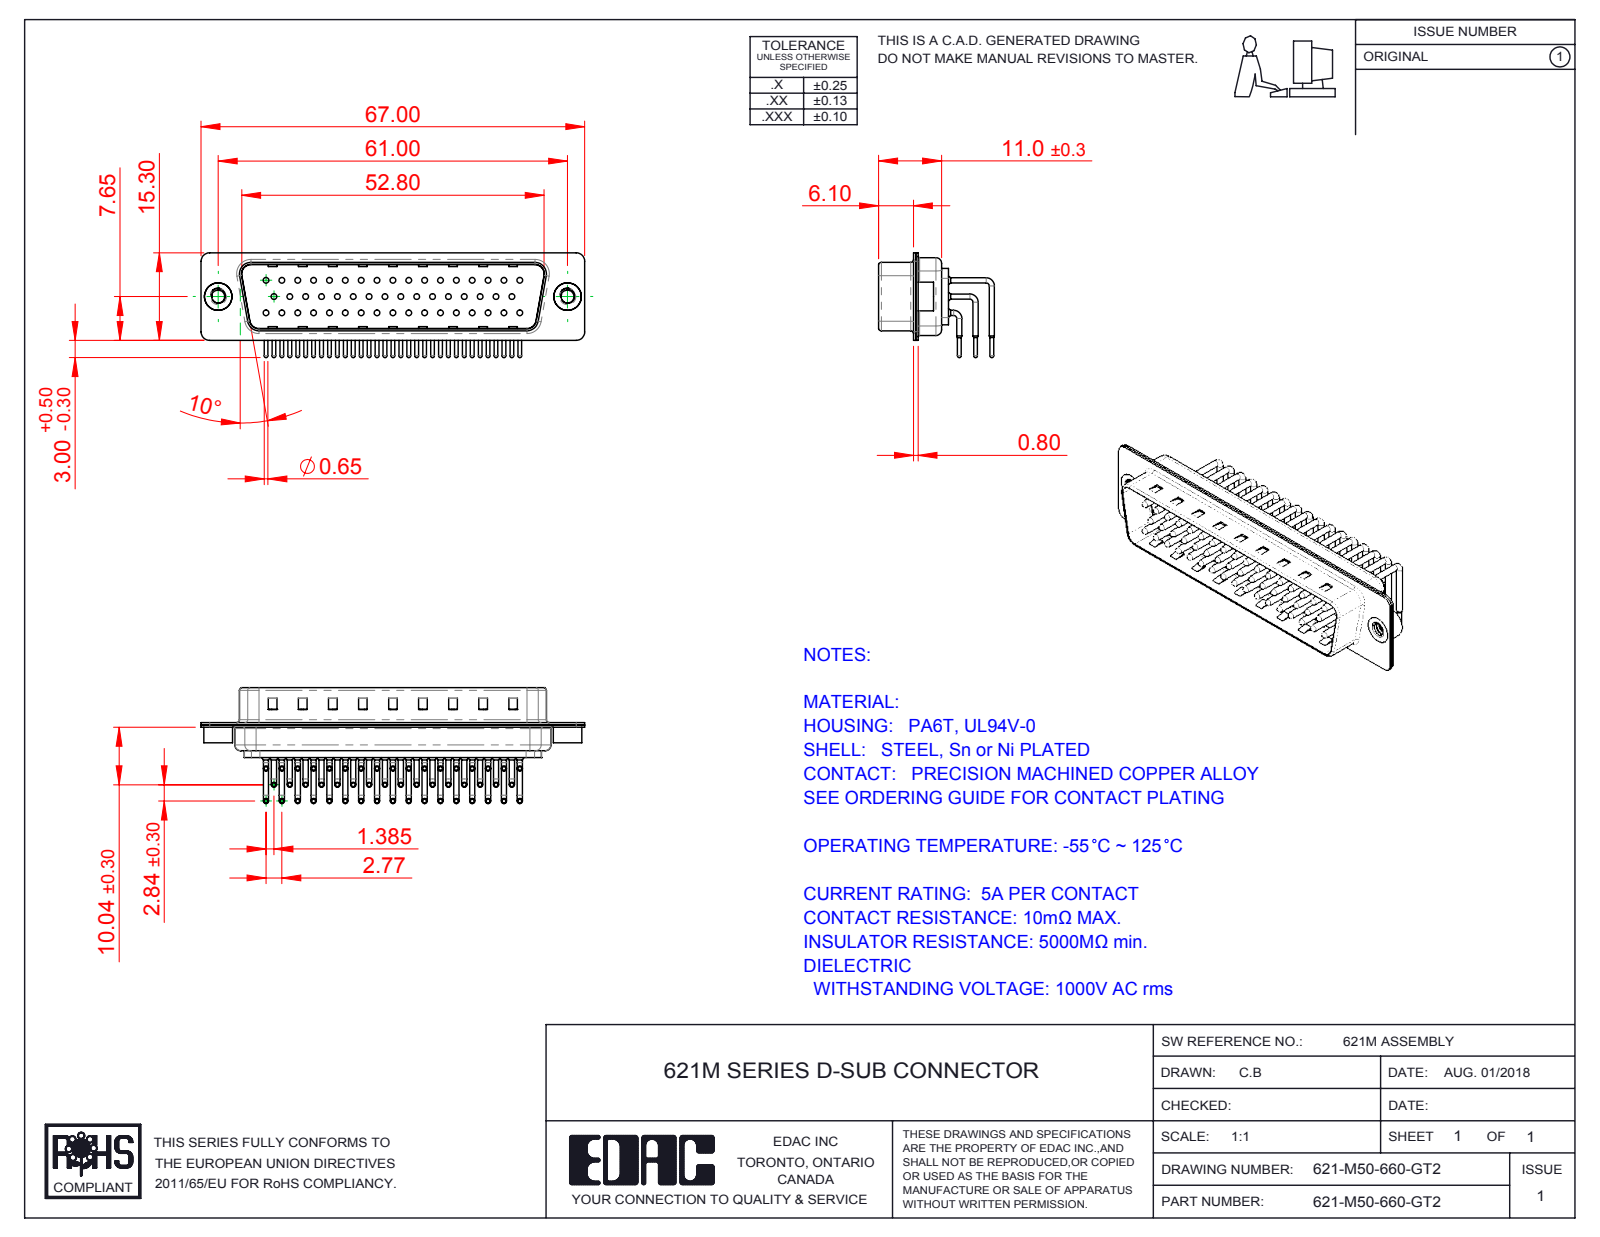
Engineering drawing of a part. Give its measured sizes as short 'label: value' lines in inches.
name: 621M Shell Front_50 Contacts; 621M Shell Rear_50 Contacts; 621M Housing_50 Contacts; 621M Contact Row 1_50 Contacts (+4 more)
written by: SolidWorks 2016 (CONFIG_CONTROL_DESIGN)
unit: in
bodies: 55 solids, 5912 faces (3403 planar, 1941 cylindrical, 568 other)
size: 2.638 × 0.796 × 0.72
volume: 0.3 in³; area: 19.49 in²
holes: 50× ⌀0.039, 50× ⌀0.067, 50× ⌀0.079, 2× ⌀0.089, 2× ⌀0.157, 2× ⌀0.189
bosses: 100× ⌀0.035, 50× ⌀0.059, 50× ⌀0.026, 2× ⌀0.197, 2× ⌀0.193
rounds: 50× R0.04, 16× R0.059, 12× R0.079, 8× R0.02, 8× R0.063, 4× R0.01, 4× R0.024, 4× R0.026
face distances: 0.016, 0.455, 0.224, 0.24, 0.487, 0.033, 0.032, 0.487, 0.52, 0.165
hole spacings: 0.109, 0.124, 0.218, 0.327, 0.436, 0.545, 0.654, 0.763
